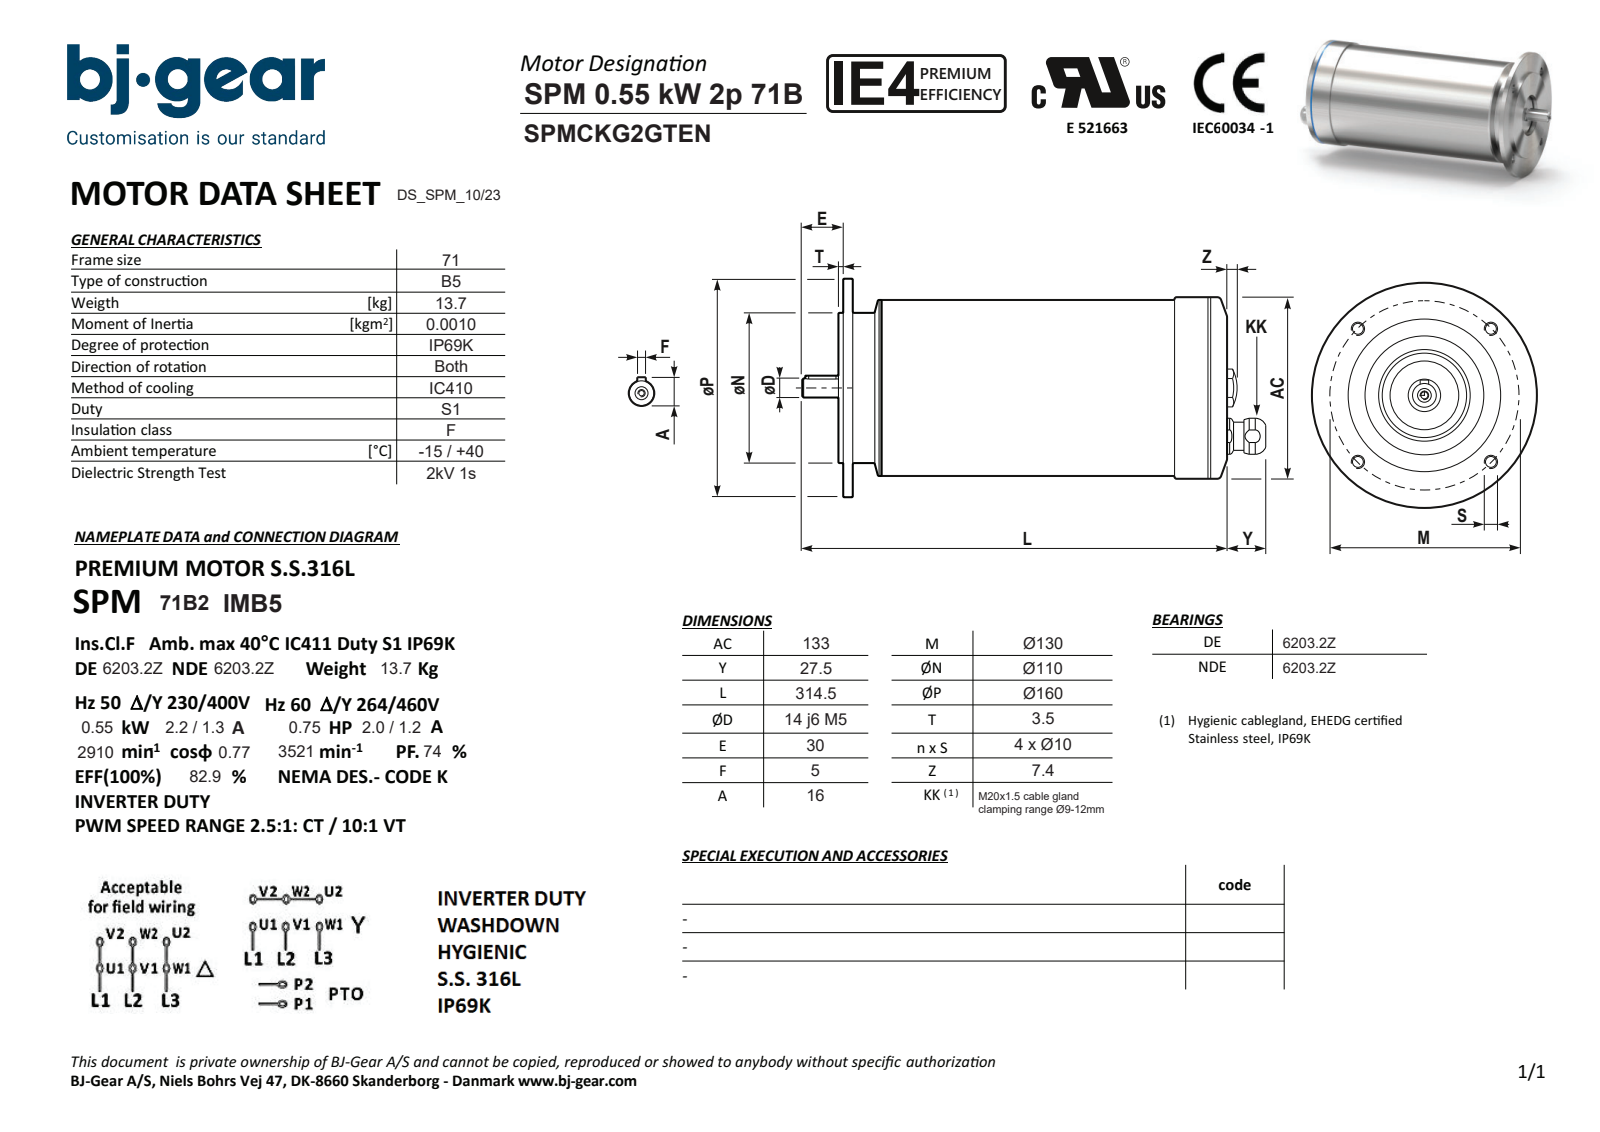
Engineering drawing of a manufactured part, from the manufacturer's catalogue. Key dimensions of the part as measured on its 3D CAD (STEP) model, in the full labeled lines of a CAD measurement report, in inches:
Part name (STEP PRODUCT): SPMCKG2GTENN4KSA1-N---NNN
STEP written by: Solid Edge (AUTOMOTIVE_DESIGN)
Units: inches
Bodies: 1 solid, 86 faces (31 planar, 30 cylindrical, 25 other)
Overall size (bounding box): 13.465 × 6.299 × 6.299
Volume: 229.2 in³ · Surface area: 259.8 in²
Round holes (diameter × count): ⌀0.394 ×4, ⌀0.163 ×1, ⌀0.209 ×1, ⌀0.276 ×1, ⌀0.528 ×1, ⌀2.047 ×1
Round bosses / shafts (diameter × count): ⌀6.299 ×1, ⌀5.236 ×1, ⌀5.235 ×1, ⌀5.079 ×1, ⌀5.078 ×1, ⌀4.331 ×1, ⌀0.787 ×1, ⌀0.669 ×1
Partial cylindrical surfaces — rounded edges, fillets, slot ends (radius × count): R0.098 ×2, R0.504 ×1
Main face-to-face distances: 0.276, 10.925, 11.201, 11.339, 0.413, 0.138, 10.984, 0.059, 0.217, 0.354
Hole centre spacings: 2.559, 3.619, 1.87, 3.631, 5.118, 1.339
